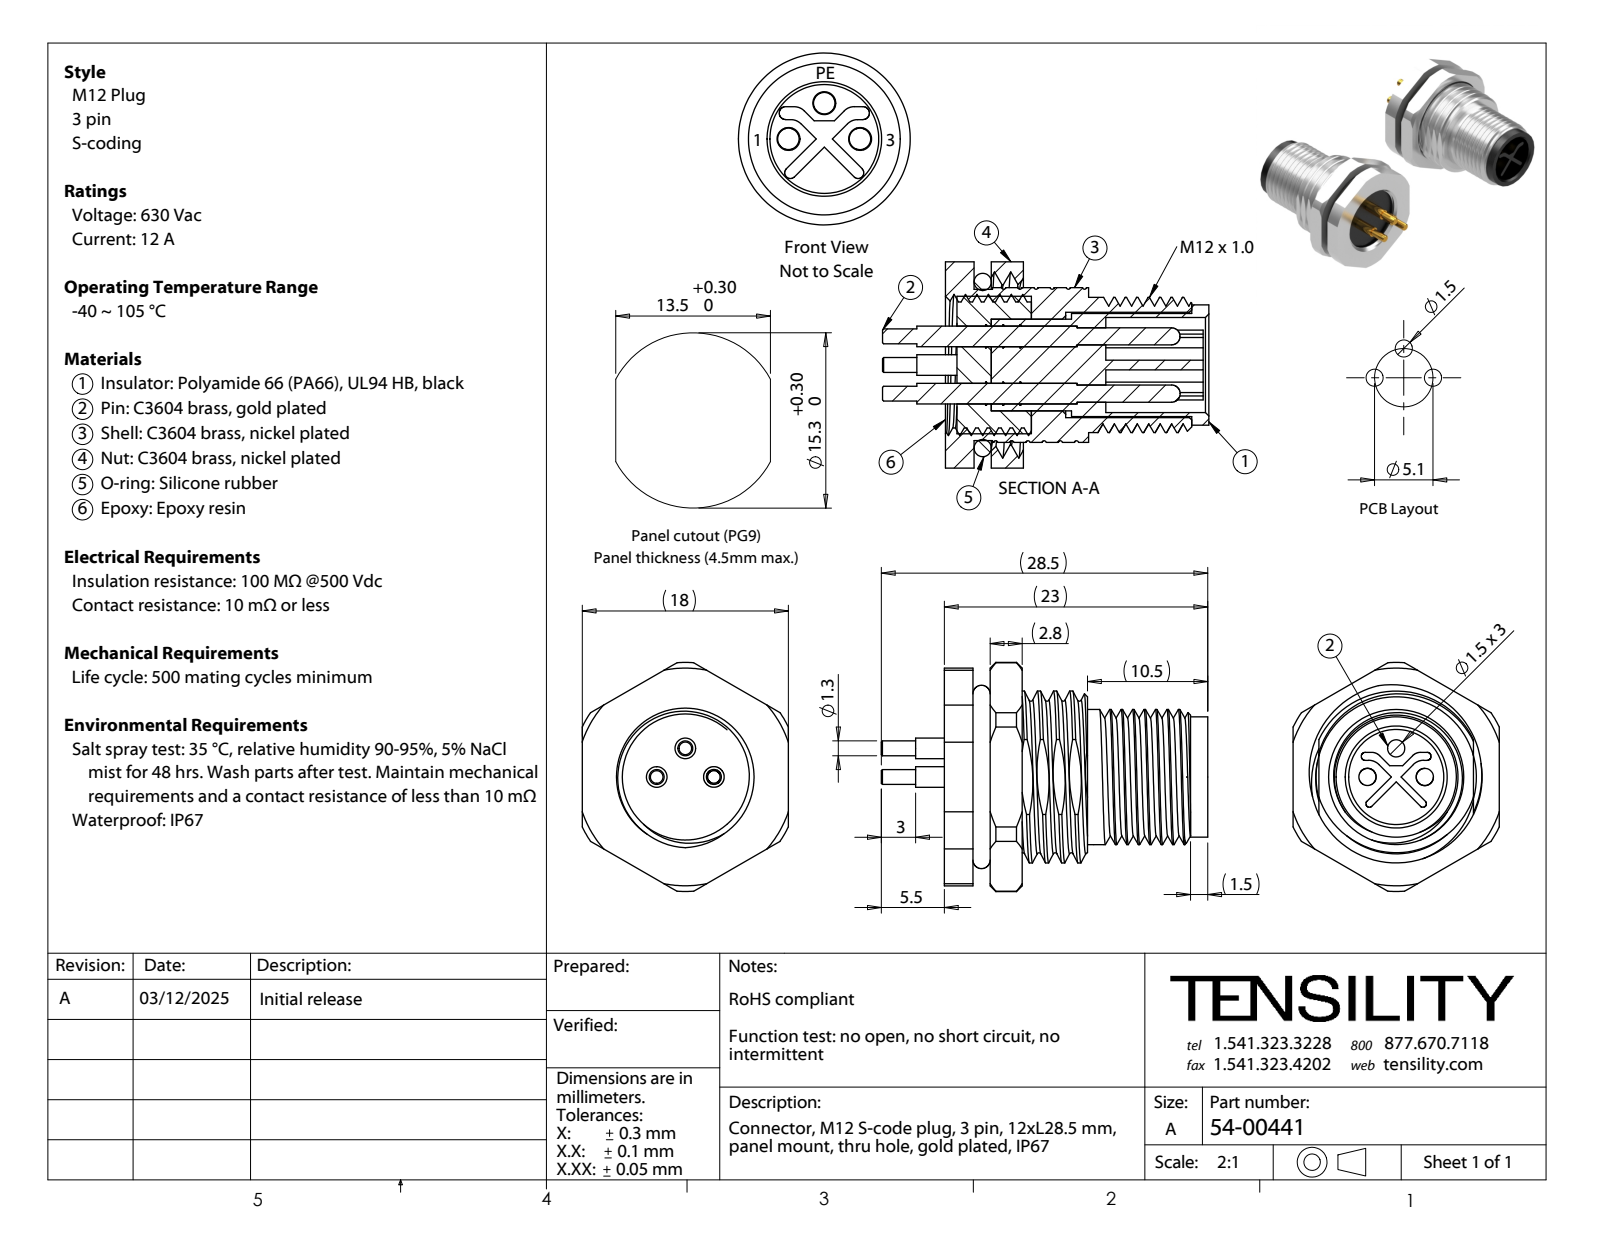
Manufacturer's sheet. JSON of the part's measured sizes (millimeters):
{"part_name": "54-00441-02; 54-00441; 54-00441-01; 54-00441-05 (+3 more)", "step_written_by": "SolidWorks 2021 (CONFIG_CONTROL_DESIGN)", "units": "millimeters", "bodies": {"solids": 8, "faces": 305, "planar": 81, "cylindrical": 140, "other": 84}, "overall_size": [28.5, 20, 18], "volume_mm3": 3143, "surface_area_mm2": 5816, "round_holes": [[1.5, 3], [8, 1], [8.3, 1], [9.2, 1], [11, 1], [14, 1]], "round_bosses_or_shafts": [[1.8, 3], [1.3, 3], [13.2, 1], [12, 1], [11.8, 1], [10.5, 1], [9, 1]], "partial_cylinders_radius": [[0.3, 2], [0.35, 2], [1, 2], [1.28, 2], [7.5, 1], [9.5, 1], [10, 1]], "face_to_face_distances": [1.5, 4, 6.5, 7.5, 5, 2.5, 3.5, 3, 1, 18], "hole_center_spacings": [2.5, 3.54, 5]}
